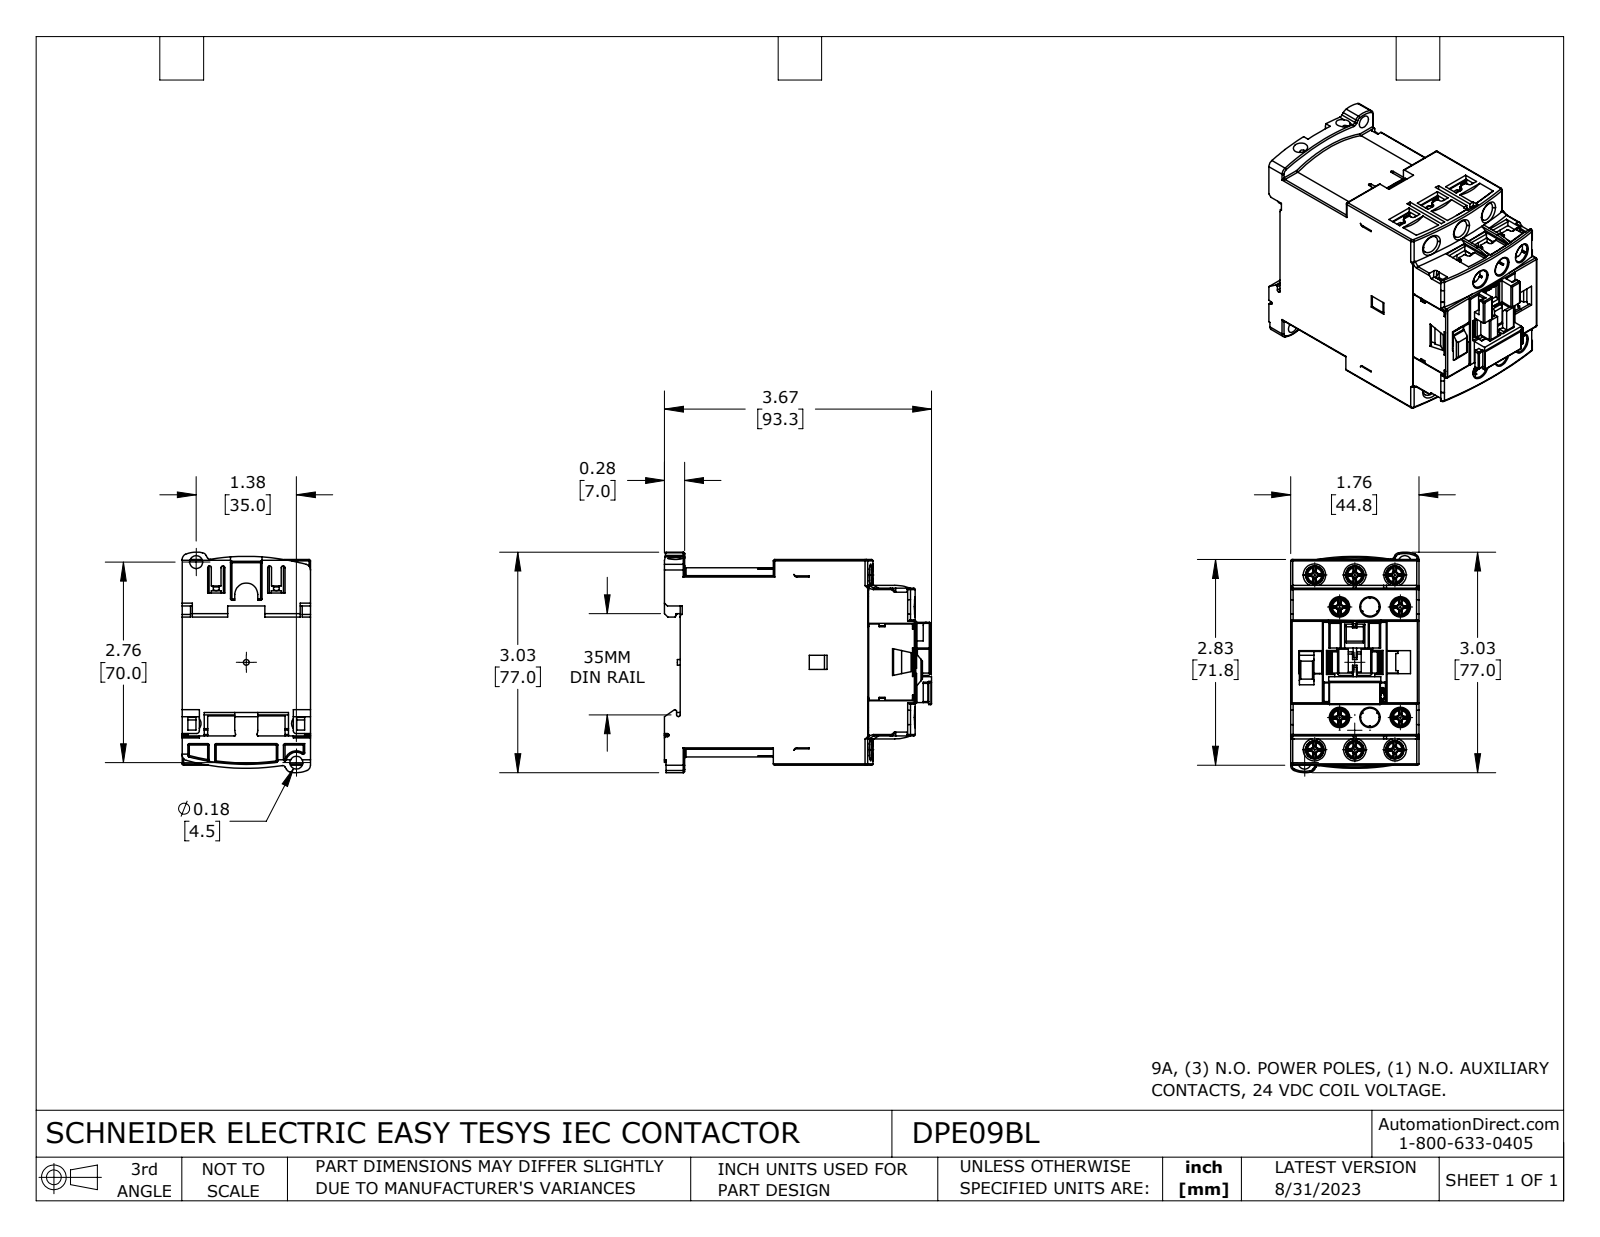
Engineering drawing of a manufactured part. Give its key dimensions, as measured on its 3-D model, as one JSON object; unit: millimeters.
{"part_name": "DPE09BL", "step_written_by": "SolidWorks 2021 (CONFIG_CONTROL_DESIGN)", "units": "millimeters", "bodies": {"solids": 10, "faces": 3575, "planar": 2470, "cylindrical": 705, "other": 400}, "overall_size": [93.2, 77, 44.8], "volume_mm3": 205300, "surface_area_mm2": 61260, "round_holes": [[6.4, 6], [6.5, 6], [1, 2], [4.5, 2], [5, 2], [2.5, 1], [4.2, 1], [6, 1]], "round_bosses_or_shafts": [[3.5, 10], [2.7, 10], [8, 6], [4, 2], [2, 1]], "partial_cylinders_radius": [[0.5, 91], [0.2, 42], [1, 34], [0.3, 31], [0.4, 22], [0.2, 14], [0.8, 10], [4, 9]], "face_to_face_distances": [44.8, 6.9, 65.5, 64.9, 1.2, 5.5, 3.8, 58, 43.6, 4.4], "hole_center_spacings": [10.6, 14, 40, 62.6, 38.6, 61, 5.7, 7]}
